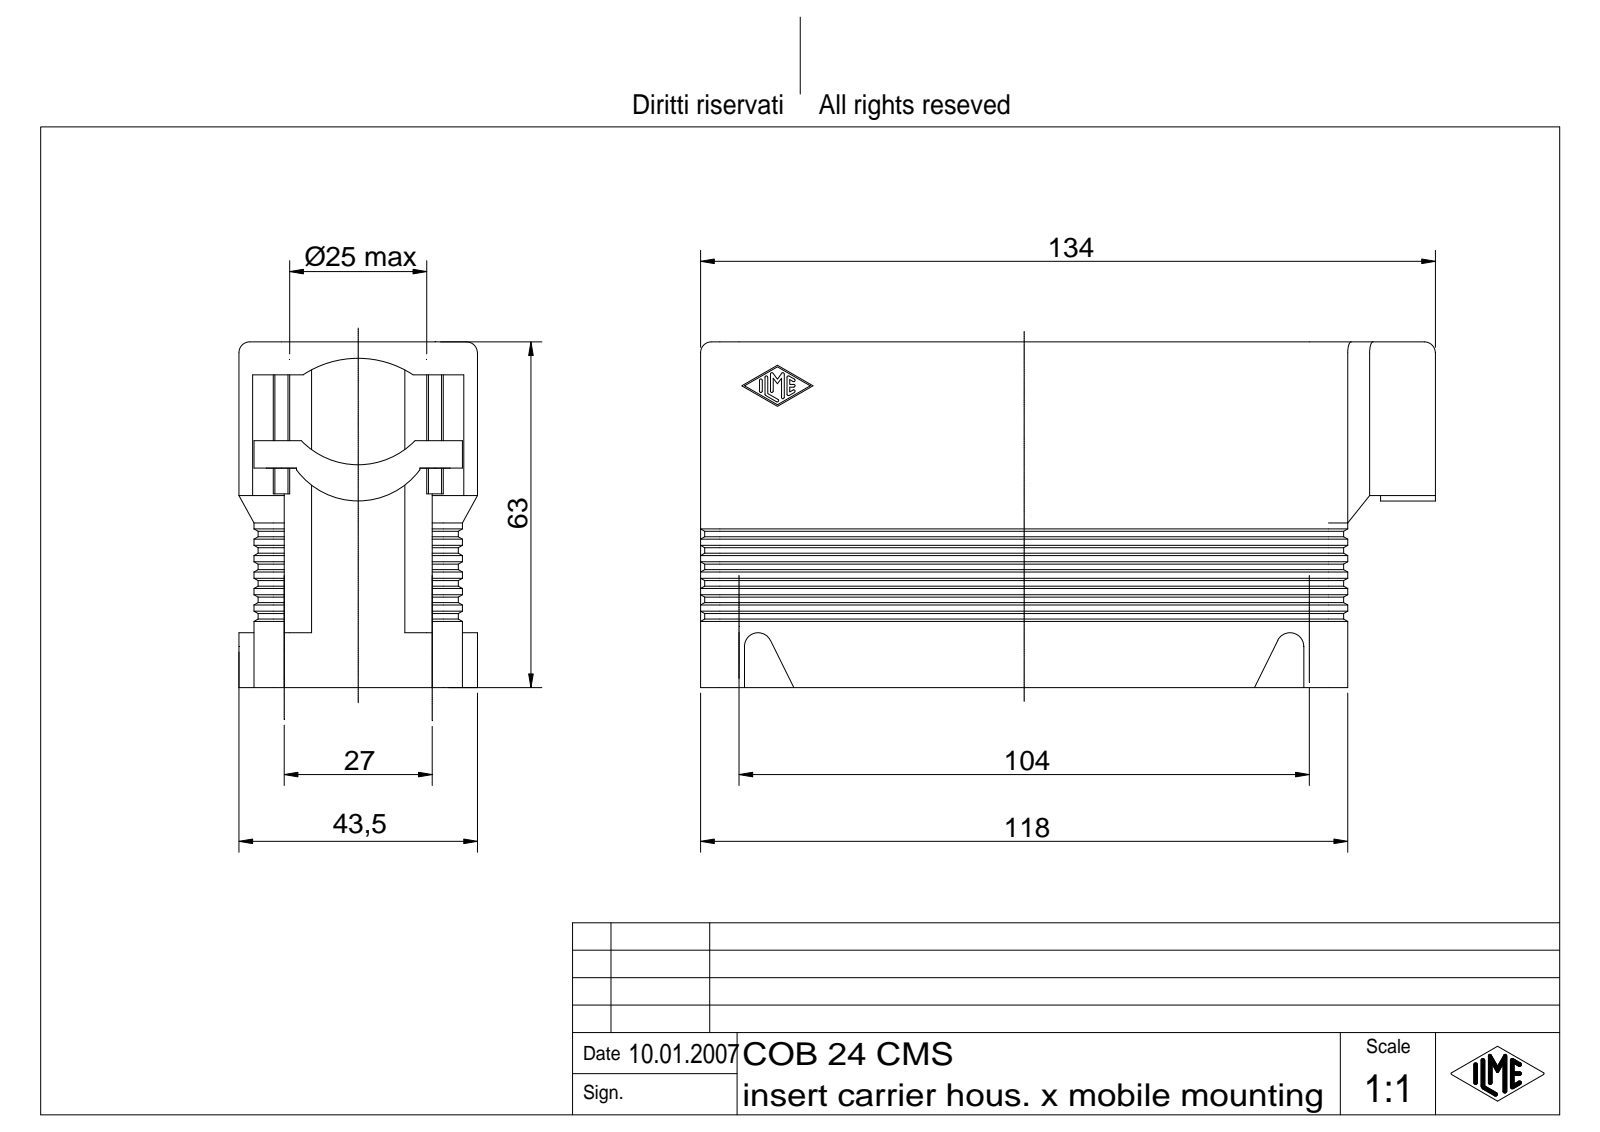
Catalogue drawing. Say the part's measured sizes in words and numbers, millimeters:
The part is named "COB 24 CMS". Its 3-D file was written by "Autodesk Inventor 7 (AUTOMOTIVE_DESIGN)". It is 6 solids with 559 faces: 217 planar, 147 cylindrical and 195 other. Overall it measures 134 by 63 by 43.5 millimeters. Its volume is 58 607 cubic millimeters and its surface area 56 257 square millimeters. Round holes: 4 of diameter 3.5. Round bosses or shafts: 4 of diameter 3.49, 1 of diameter 5.2, 1 of diameter 3. Partial cylindrical surfaces (rounded edges, fillets, slot ends): 14 of radius 0.25, 10 of radius 2, 4 of radius 1.5, 4 of radius 3.5, 4 of radius 4, 4 of radius 5, 2 of radius 0.5, 2 of radius 2.5. The main face-to-face distances are 2, 36, 34, 38, 3, 35.25, 4.75, 2.6, 3.5, 0.75. The hole center spacings are 27, 104, 107.45.
